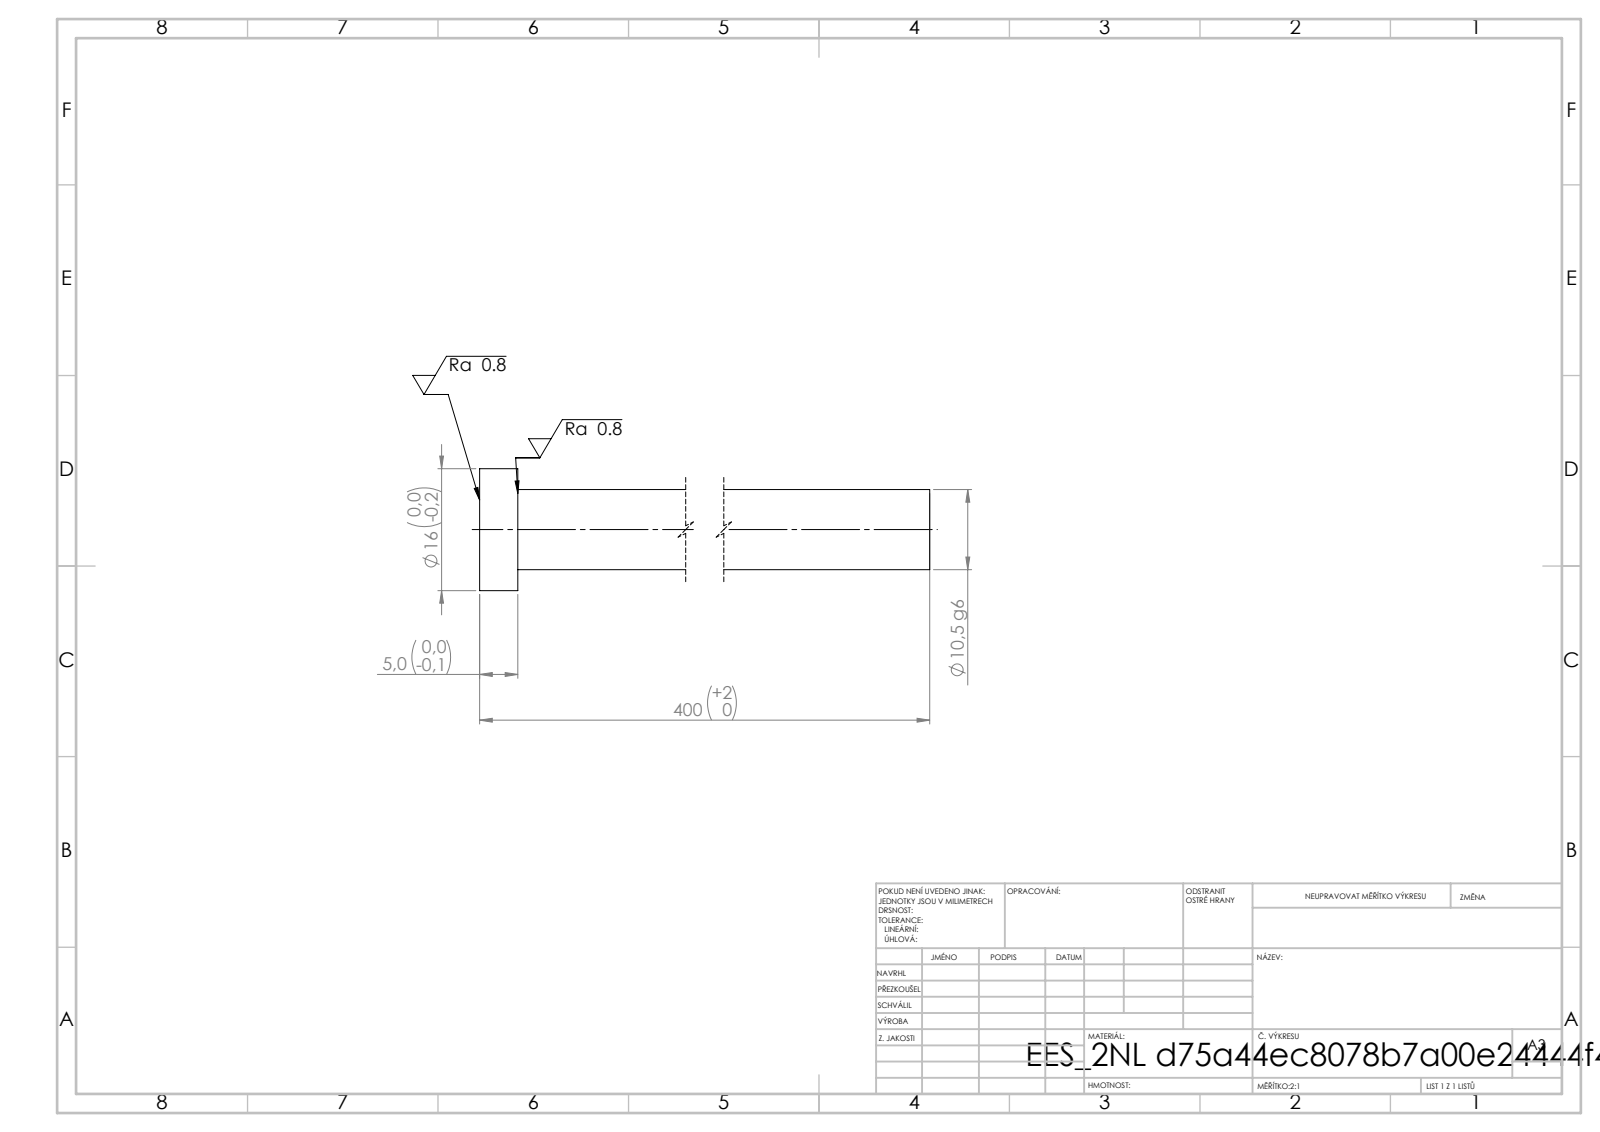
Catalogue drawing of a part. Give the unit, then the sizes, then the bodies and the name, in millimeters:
Units: millimetres
Overall size (bounding box): 400 × 16 × 16
Round bosses / shafts (diameter × count): ⌀16 ×1, ⌀10.5 ×1
Main face-to-face distances: 5, 400, 395
Volume: 35 208 mm³ · Surface area: 13 683 mm²
Bodies: 1 solid, 7 faces (3 planar, 4 cylindrical, 0 other)
STEP written by: SolidWorks 2019 (CONFIG_CONTROL_DESIGN)
